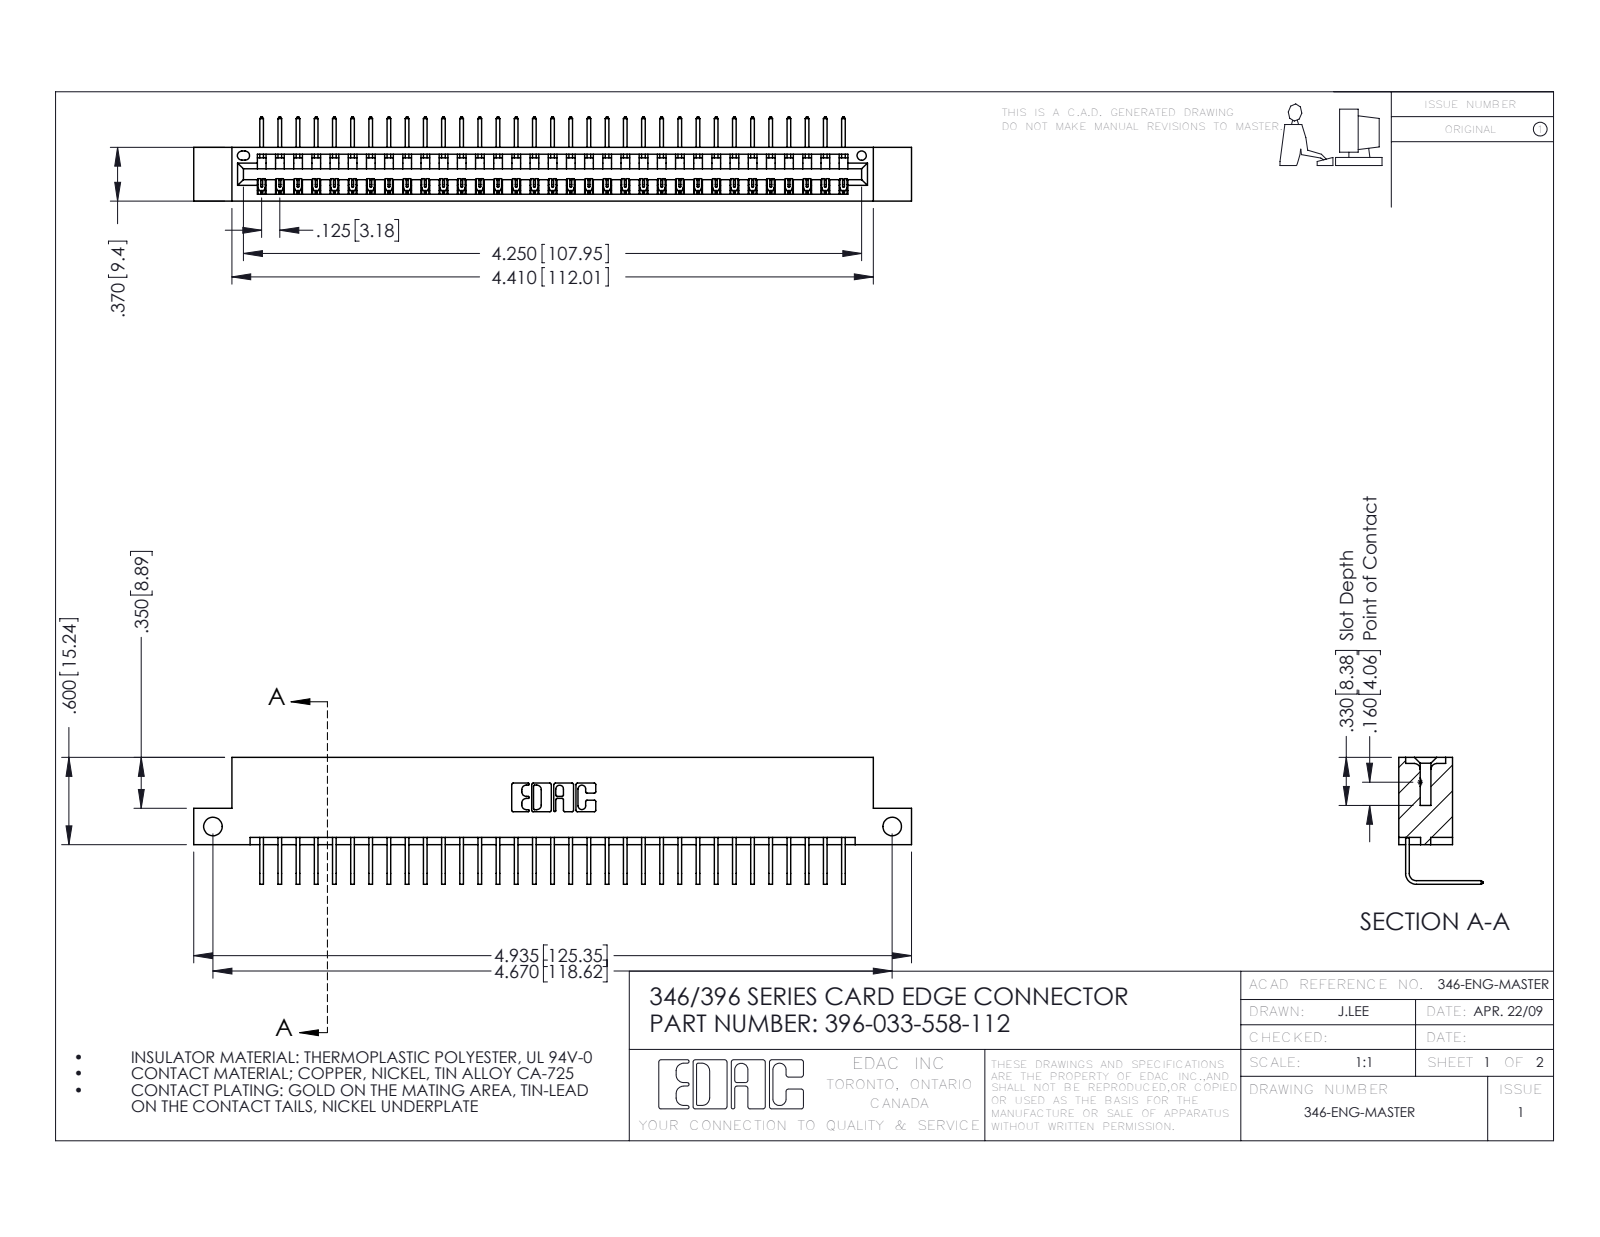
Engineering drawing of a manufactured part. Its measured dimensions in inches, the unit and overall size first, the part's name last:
Units: inches
Overall size (bounding box): 4.935 × 0.873 × 0.58
Round holes (diameter × count): ⌀0.128 ×2, ⌀0.064 ×1
Partial cylindrical surfaces — rounded edges, fillets, slot ends (radius × count): R0.006 ×66, R0.01 ×22, R0.007 ×6, R0.031 ×6, R0.026 ×3, R0.031 ×2, R0.04 ×2, R0.014 ×1
Main face-to-face distances: 0.322, 0.048, 0.37, 0.25, 0.298, 0.025, 0.072, 0.148, 0.222, 0.1
Hole centre spacings: 4.67
Volume: 0.73 in³ · Surface area: 23.81 in²
Bodies: 34 solids, 2102 faces (1462 planar, 640 cylindrical, 0 other)
Part name (STEP PRODUCT): 345-292-001_558 Tail - 2; 346 Part_Flush Mounting Lugs - Side Mount; 396-033-558-112
STEP written by: SolidWorks 2016 (CONFIG_CONTROL_DESIGN)
